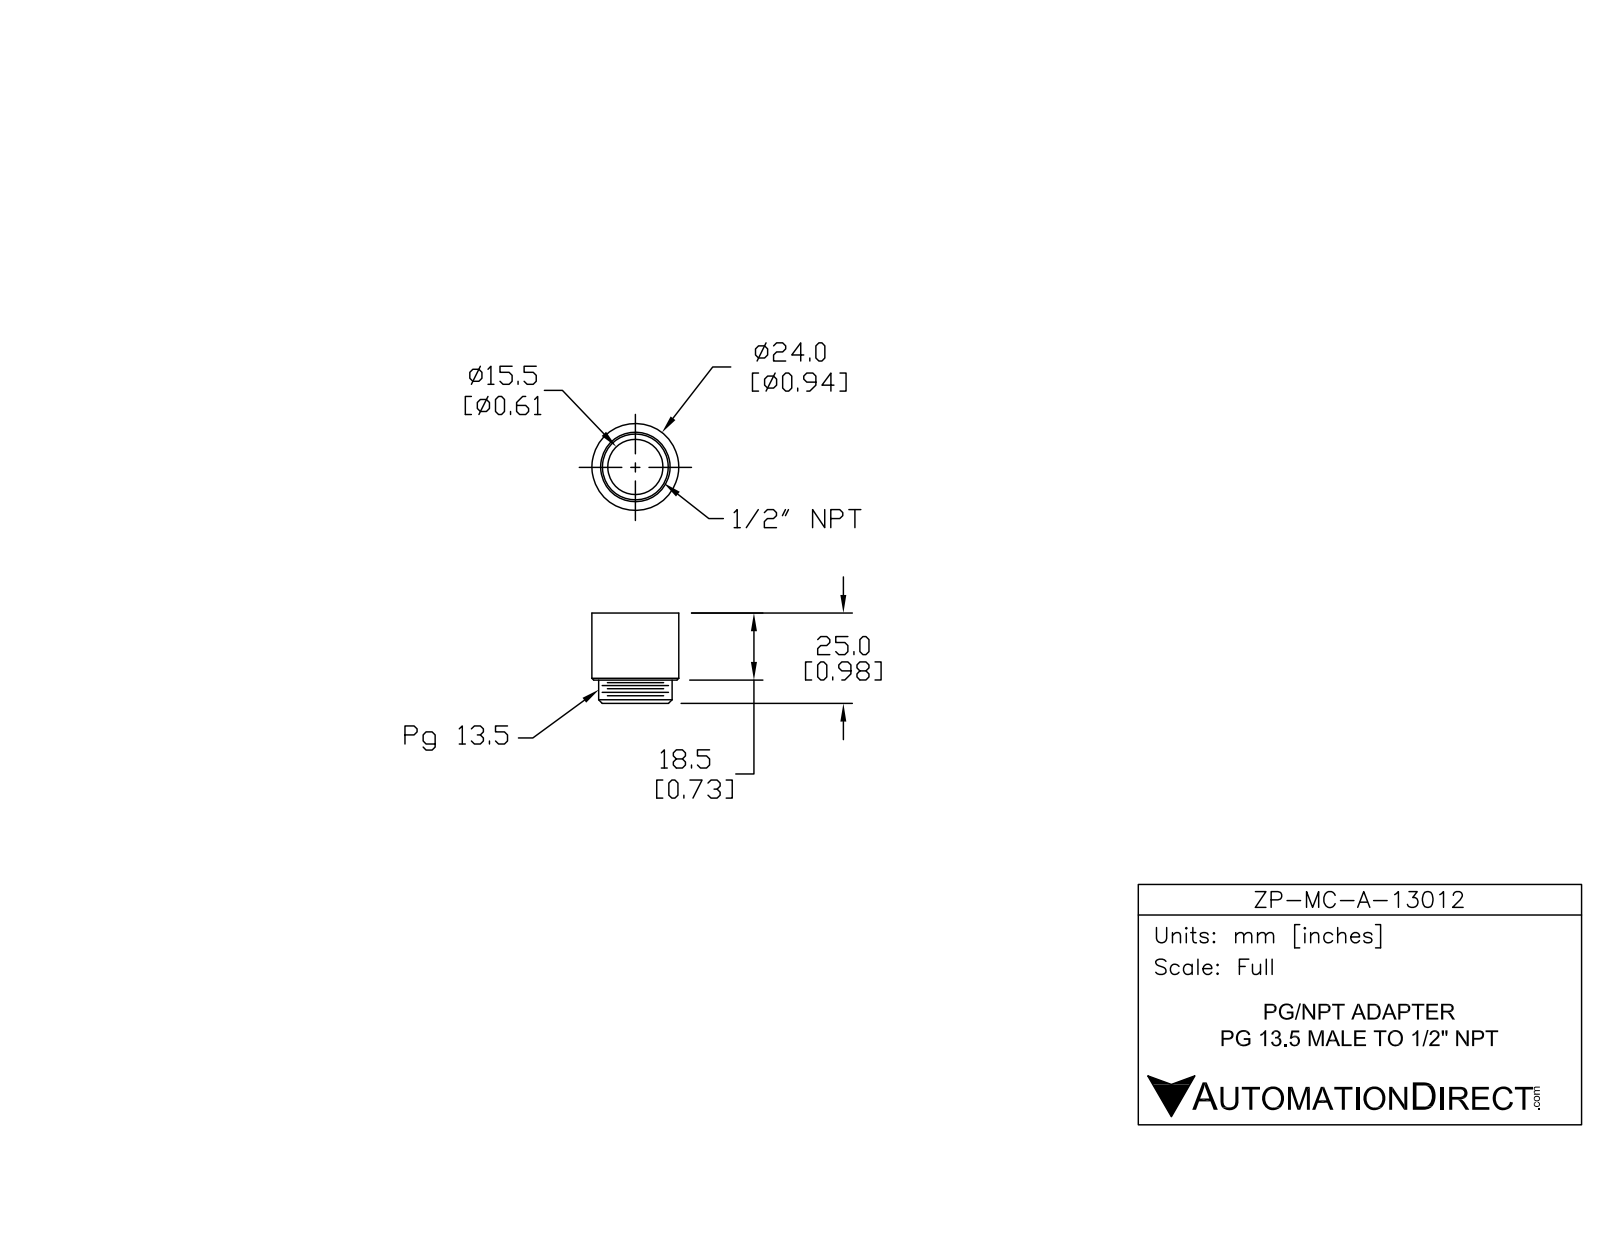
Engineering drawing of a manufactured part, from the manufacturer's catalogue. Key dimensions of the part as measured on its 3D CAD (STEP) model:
Part name (STEP PRODUCT): ZP-MC-A-13012
STEP written by: SolidWorks 2014 (AUTOMOTIVE_DESIGN)
Units: millimetres
Bodies: 1 solid, 18 faces (4 planar, 8 cylindrical, 6 other)
Overall size (bounding box): 25 × 24 × 24
Volume: 4 636 mm³ · Surface area: 3 604 mm²
Round holes (diameter × count): ⌀15.5 ×1, ⌀18.2 ×1
Round bosses / shafts (diameter × count): ⌀24 ×1, ⌀20.3 ×1
Main face-to-face distances: 18.5, 6.5, 25, 10, 3.5, 15
